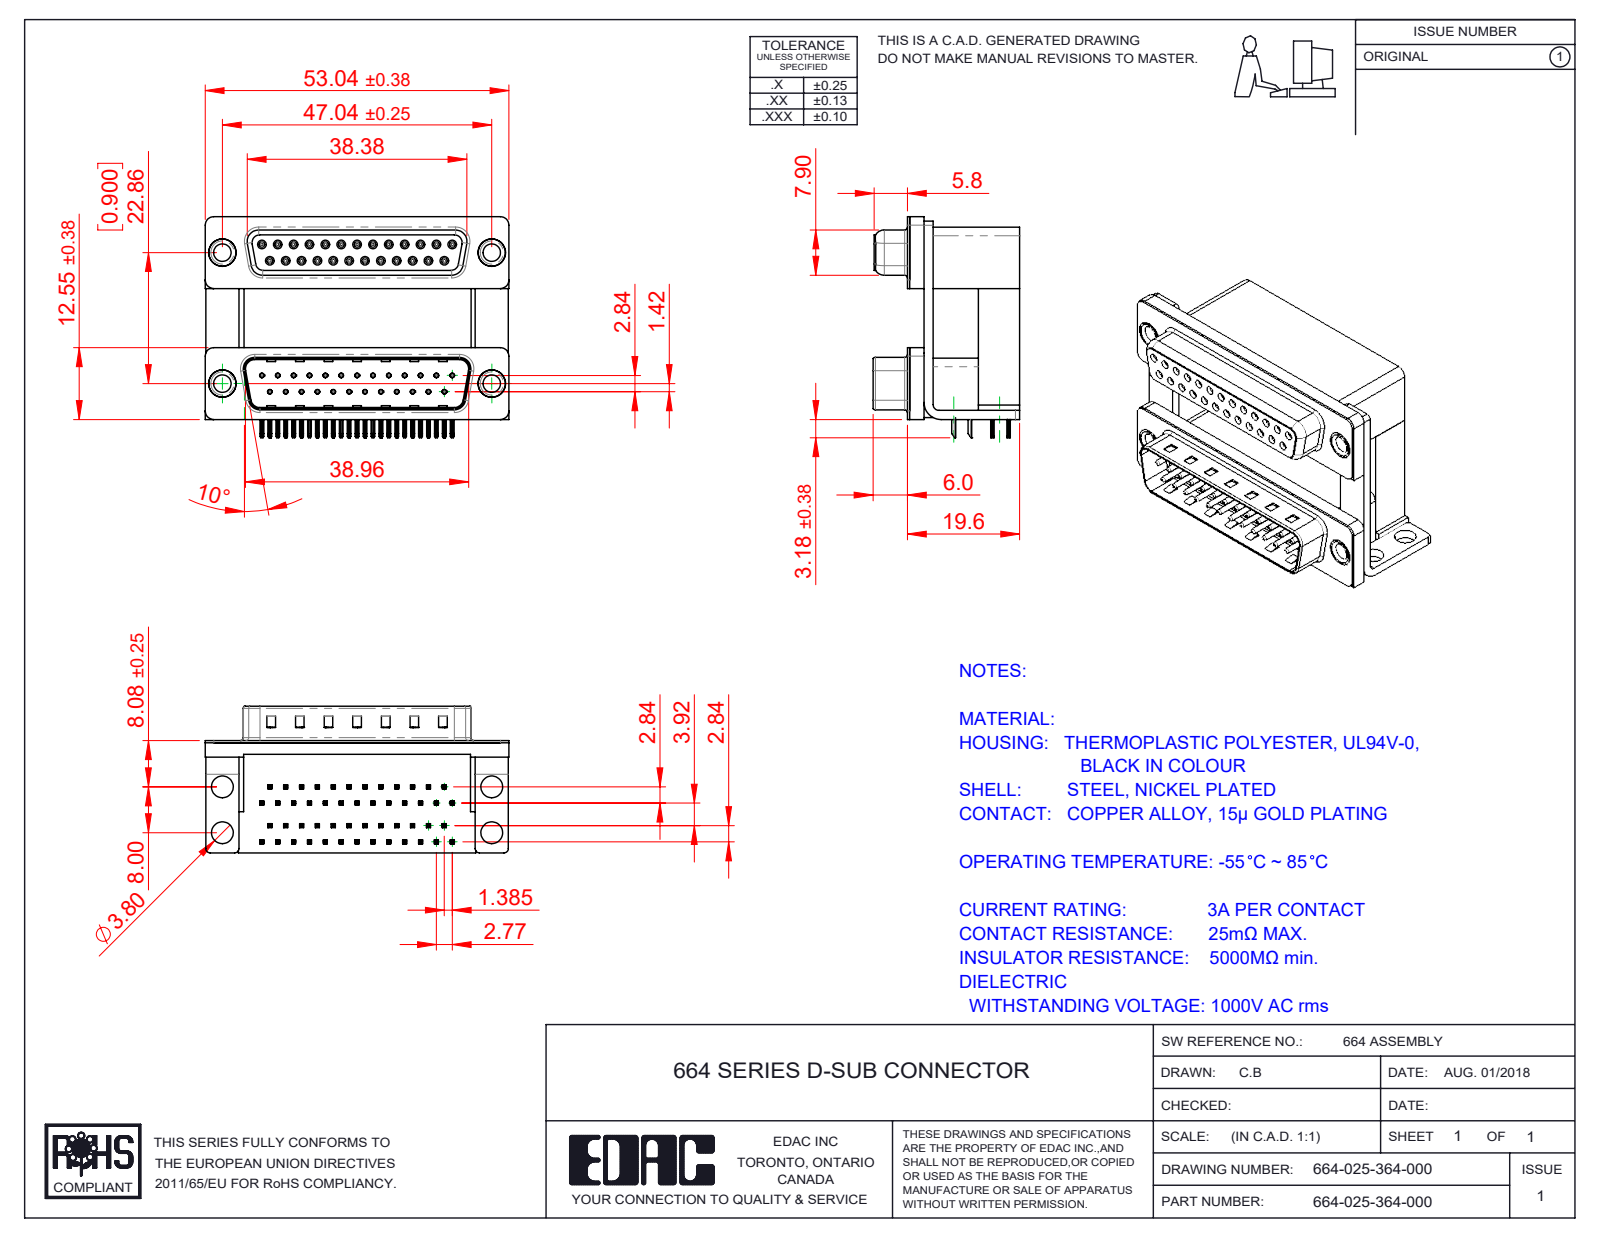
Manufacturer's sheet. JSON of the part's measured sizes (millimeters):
{"part_name": "664-025-364-000; 664 Shell Plug_25 Contacts; 664 Thru Hole Rivet; 664 Contact Bottom Lower (+8 more)", "step_written_by": "SolidWorks 2020 (CONFIG_CONTROL_DESIGN)", "units": "millimeters", "bodies": {"solids": 61, "faces": 6119, "planar": 3257, "cylindrical": 1507, "other": 1355}, "overall_size": [53.04, 38.59, 25.6], "volume_mm3": 23583, "surface_area_mm2": 25011, "round_holes": [[0.8, 50], [0.35, 25], [0.9, 25], [3.05, 4], [3.5, 4], [3.8, 4], [4, 4], [4.8, 4], [5, 4]], "round_bosses_or_shafts": [[1.2, 25], [0.75, 25], [4.9, 4], [4.75, 4], [3.85, 4]], "partial_cylinders_radius": [[0.1, 200], [0.15, 100], [0.25, 100], [0.12, 50], [0.35, 50], [0.34, 25], [1.5, 14], [0.28, 12]], "face_to_face_distances": [19.2, 12, 0.4, 7.2, 10.7, 2.84, 16.7, 9.5, 2.5, 12.4], "hole_center_spacings": [2.77, 3.16, 5.54, 8.31, 11.08, 13.85, 16.62, 5.03]}
